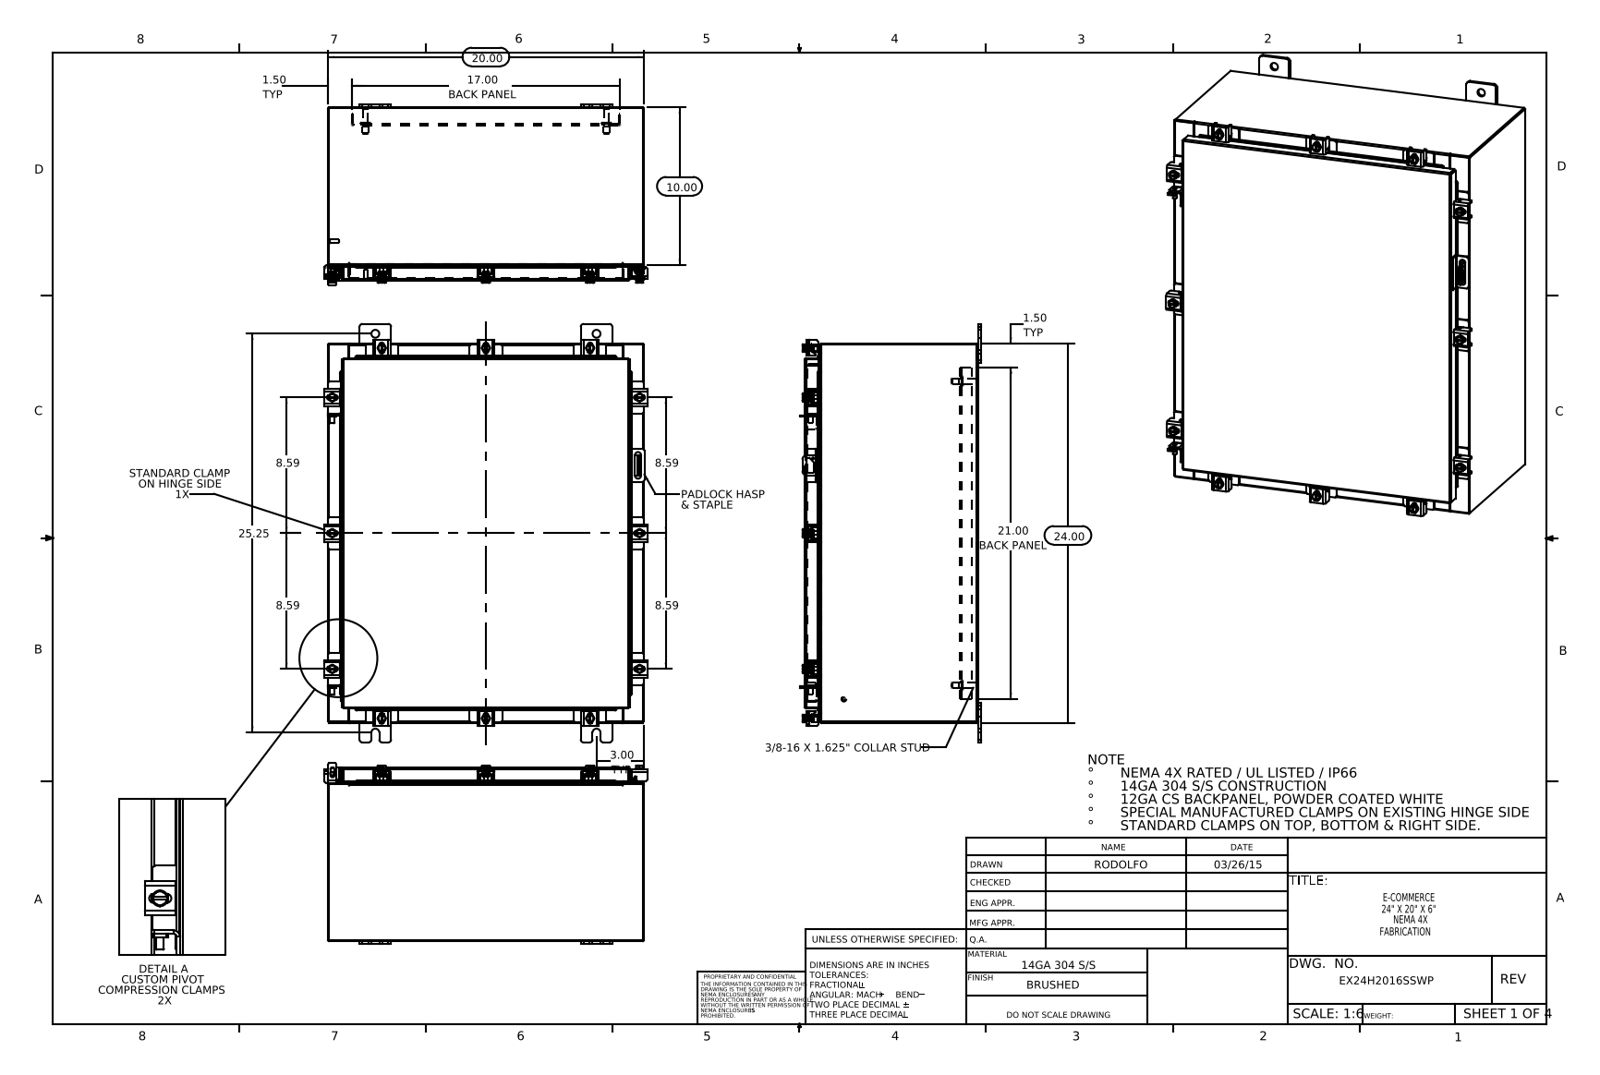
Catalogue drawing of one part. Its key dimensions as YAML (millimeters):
part_name: "22104005_DEFAULT_RTP30; Special Clamp Assembly; EX24H2016SSWP Special Clamp; EX24H2016SSWP Cover (+8 more)"
step_written_by: "SolidWorks 2014 (CONFIG_CONTROL_DESIGN)"
units: millimeters
bodies: {solids: 81, faces: 2018, planar: 1075, cylindrical: 783, other: 160}
overall_size: [673.1, 518.7, 290.9]
volume: 3282000
surface_area: 3250000
round_holes:
  - {diameter: 5.4, count: 12}
  - {diameter: 6.6, count: 12}
  - {diameter: 12.7, count: 8}
  - {diameter: 3.2, count: 1}
  - {diameter: 6.4, count: 1}
round_bosses_or_shafts:
  - {diameter: 12.7, count: 12}
  - {diameter: 6.4, count: 12}
  - {diameter: 10.1, count: 10}
  - {diameter: 15.9, count: 4}
  - {diameter: 9.5, count: 4}
  - {diameter: 8.4, count: 4}
  - {diameter: 8, count: 2}
  - {diameter: 6, count: 2}
partial_cylinders:
  - {radius: 1.5, count: 54}
  - {radius: 0.3, count: 24}
  - {radius: 3.6, count: 24}
  - {radius: 4.8, count: 24}
  - {radius: 2.2, count: 22}
  - {radius: 3, count: 22}
  - {radius: 2.3, count: 18}
  - {radius: 1.3, count: 17}
face_to_face_distances: [1.9, 276.9, 506.1, 278.8, 275, 607.7, 2.6, 25.4, 27.3, 249.6]
hole_center_spacings: [59.4, 112.5, 167.5, 218.3, 259.5, 308.3, 386.9, 422.1]
